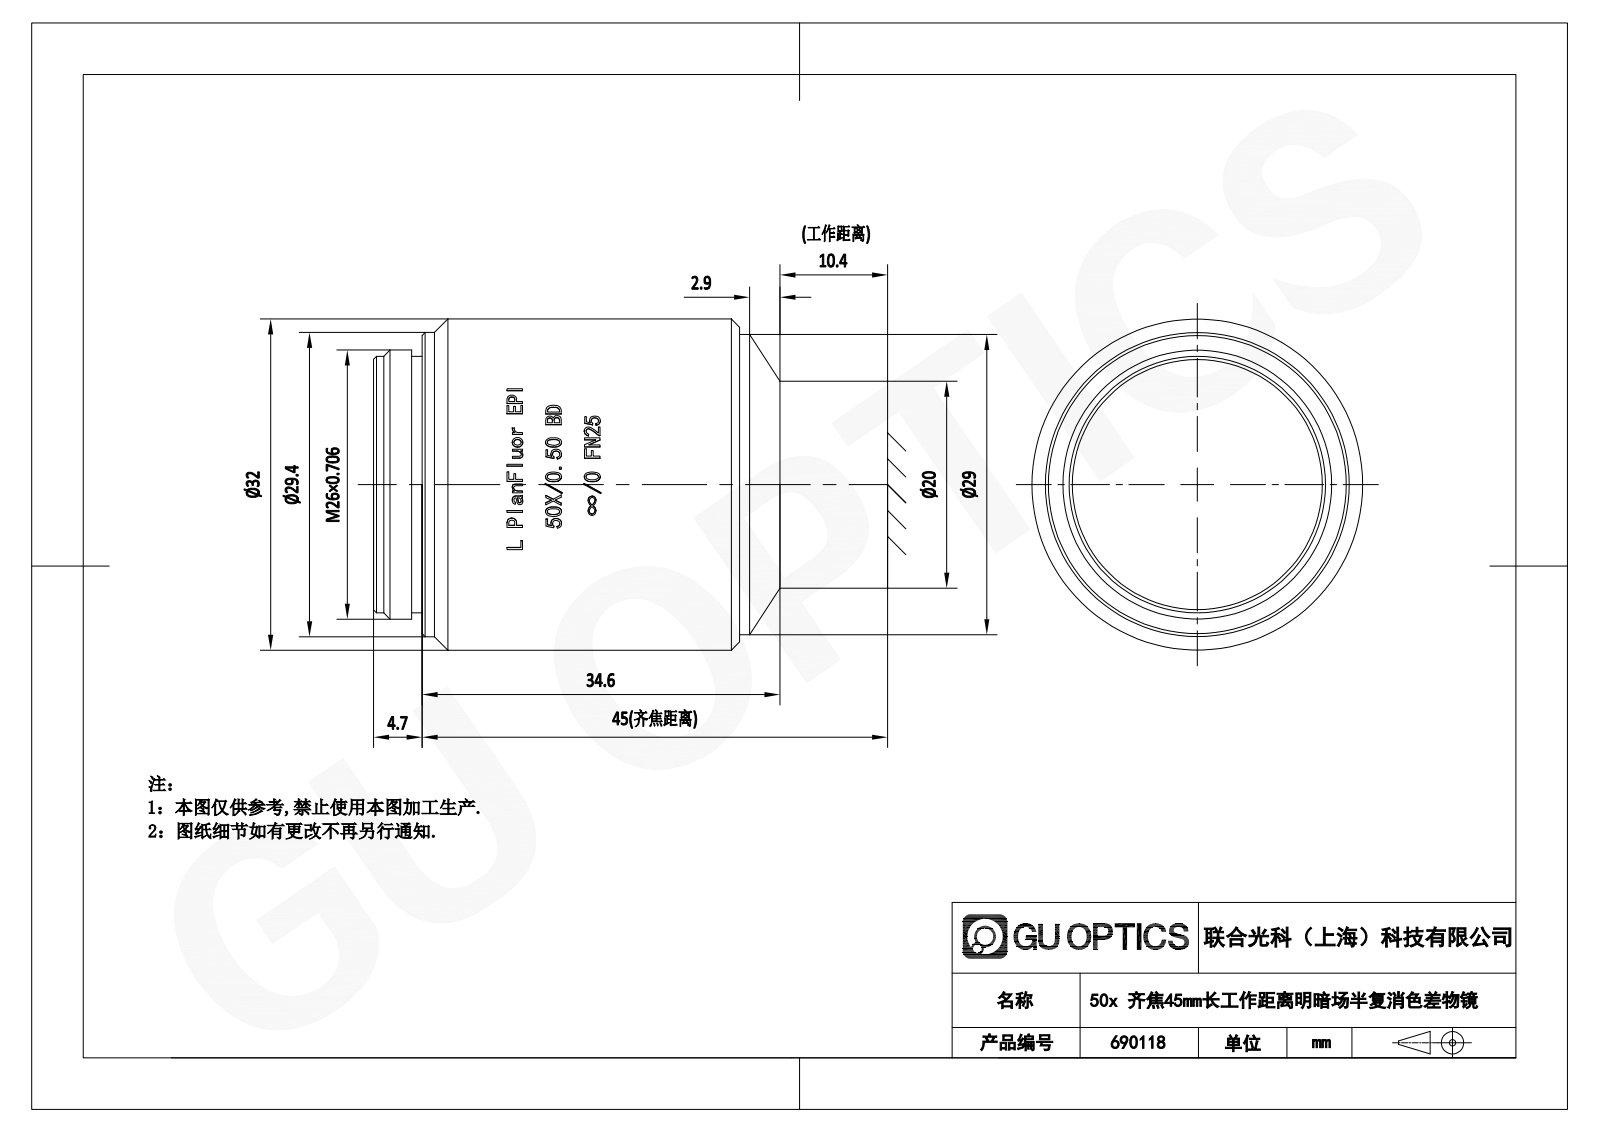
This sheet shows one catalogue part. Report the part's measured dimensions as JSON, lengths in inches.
{"part_name": "690118", "step_written_by": "SolidWorks 2020 (CONFIG_CONTROL_DESIGN)", "units": "inches", "bodies": {"solids": 1, "faces": 345, "planar": 147, "cylindrical": 55, "other": 143}, "overall_size": [1.547, 1.262, 1.26], "volume_in3": 1.76, "surface_area_in2": 7.959, "round_bosses_or_shafts": [[1.26, 1], [1.157, 1], [1.142, 1], [1.024, 1], [0.976, 1]], "partial_cylinders_radius": [[0.632, 1]], "face_to_face_distances": [1.547, 0.185, 1.362, 1.394, 1.209, 0.154, 0.146, 0.039, 1.248, 1.402]}
